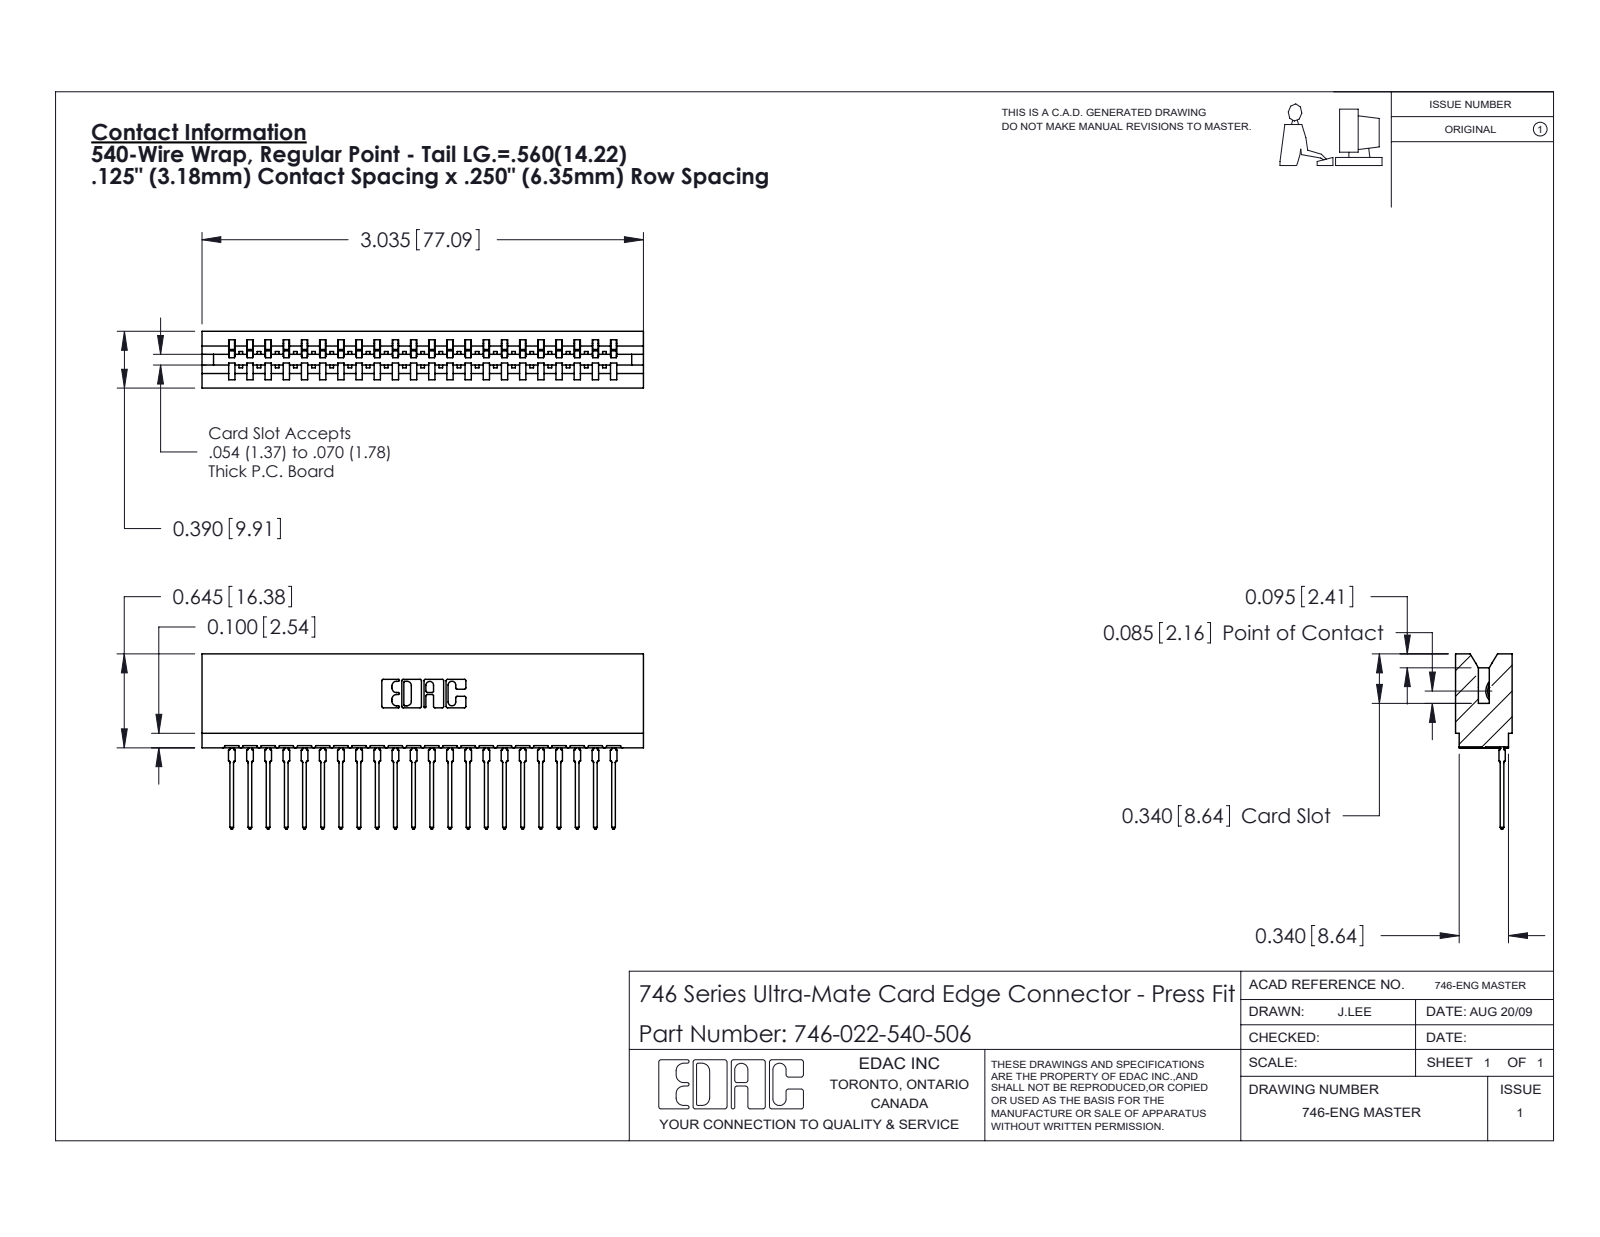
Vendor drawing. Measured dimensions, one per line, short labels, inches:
name: 746-292-001_540; 746 Part_.340 Slot Depth - 06; 746-022-540-506
written by: SolidWorks 2020 (CONFIG_CONTROL_DESIGN)
unit: in
bodies: 23 solids, 2474 faces (1442 planar, 460 cylindrical, 572 other)
size: 3.035 × 1.204 × 0.39
volume: 0.537 in³; area: 18.37 in²
rounds: 44× R0.021, 23× R0.015, 22× R0.01, 6× R0.007, 6× R0.031, 4× R0.005, 4× R0.011, 3× R0.026
face distances: 0.25, 0.057, 0.333, 0.39, 0.5, 0.025, 0.307, 0.042, 0.125, 0.083
